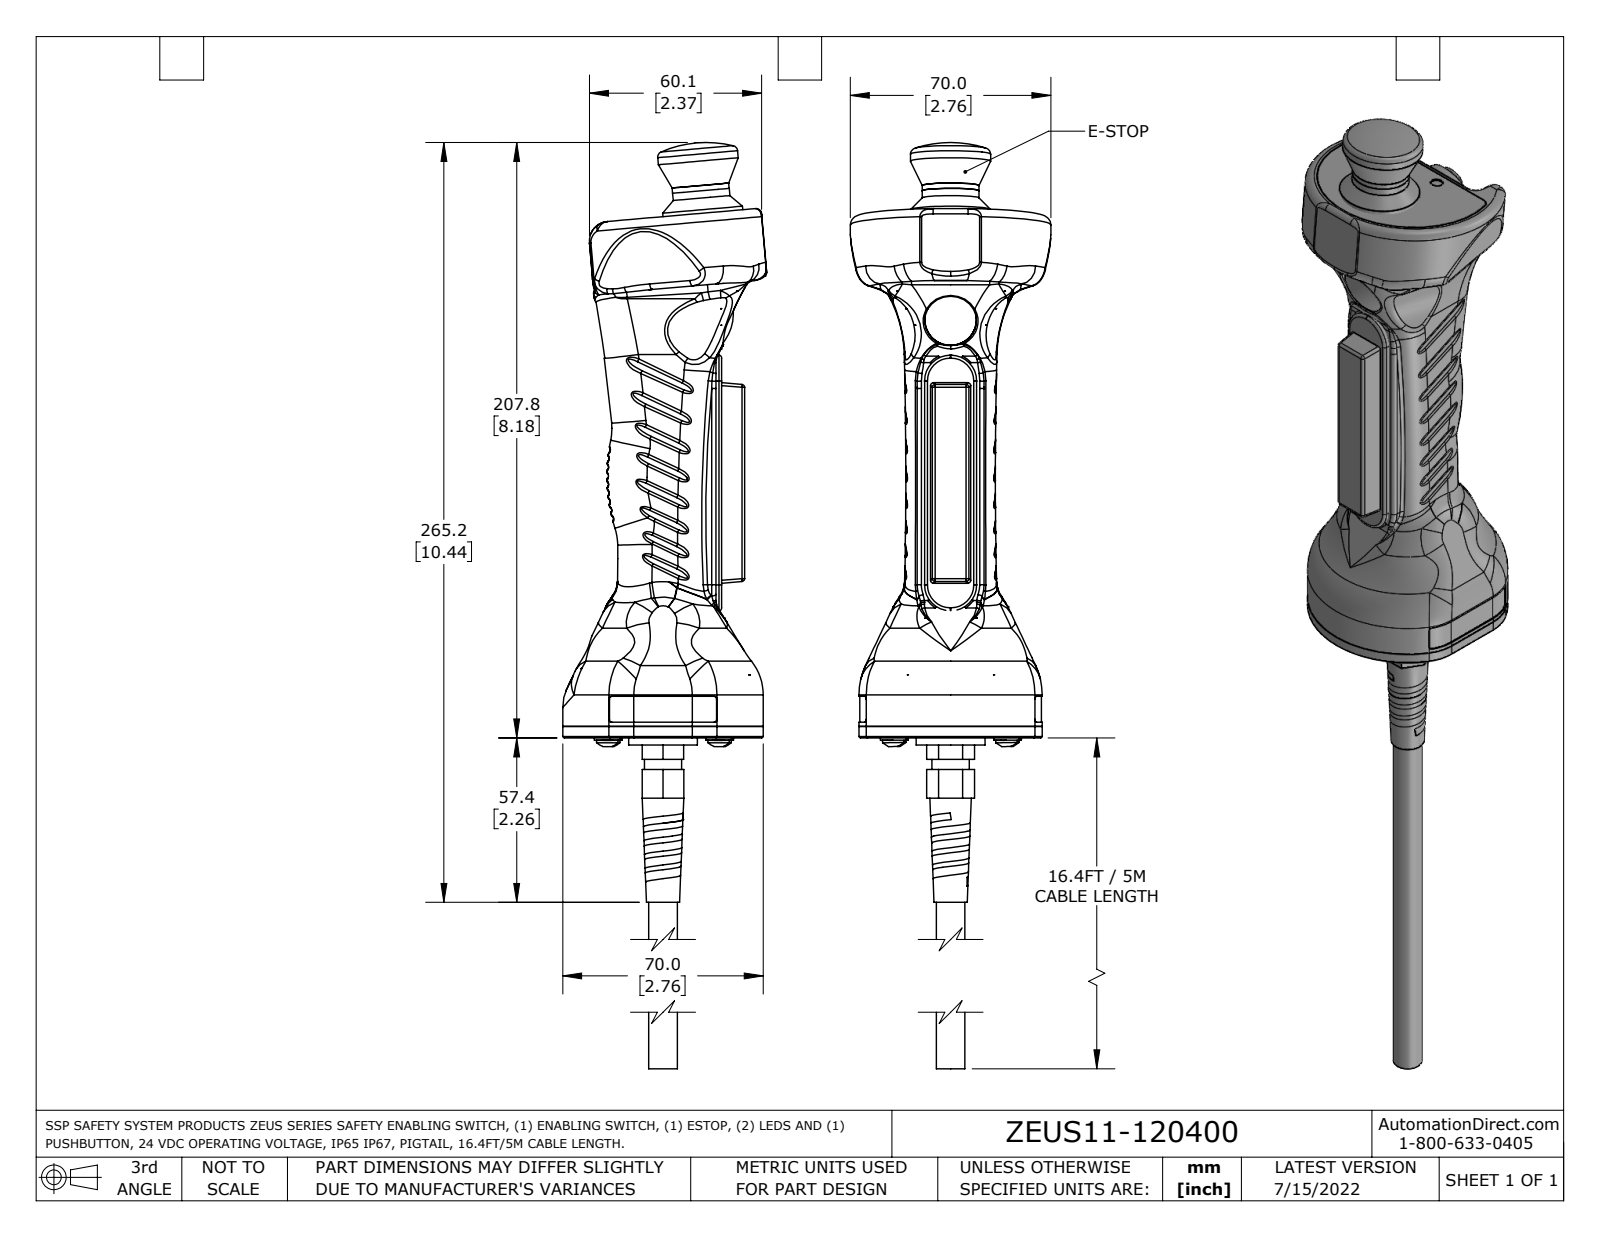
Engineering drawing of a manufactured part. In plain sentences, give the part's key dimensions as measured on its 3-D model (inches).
The part is named "ZEUS11-120400". Its 3-D file was written by "SolidWorks 2021 (AUTOMOTIVE_DESIGN)". It is 21 solids with 1397 faces: 480 planar, 462 cylindrical and 455 other. Overall it measures 15.833 by 2.803 by 2.756 inches. Its volume is 24.73 cubic inches and its surface area 137.4 square inches. Round holes: 4 of diameter 0.132, 4 of diameter 0.169, 4 of diameter 0.177, 4 of diameter 0.197, 2 of diameter 0.098, 2 of diameter 0.11, 2 of diameter 0.165, 2 of diameter 0.173, 2 of diameter 0.331, 1 of diameter 0.039, 1 of diameter 0.159, 1 of diameter 0.201. Round bosses or shafts: 4 of diameter 0.354, 4 of diameter 0.295, 4 of diameter 0.157, 4 of diameter 0.039, 2 of diameter 1.102, 2 of diameter 0.781, 2 of diameter 0.461, 2 of diameter 0.236. Partial cylindrical surfaces (rounded edges, fillets, slot ends): 96 of radius 0.005, 51 of radius 0.039, 48 of radius 0.028, 22 of radius 0.008, 21 of radius 0.079, 10 of radius 0.118, 8 of radius 0.006, 7 of radius 0.031. The main face-to-face distances are 0.157, 0.079, 0.014, 0.02, 0.065, 0.059, 0.098, 0.039, 0.177, 0.571. The hole center spacings are 0.404, 0.63, 0.867, 1.08, 1.181, 1.531, 1.558, 0.513.
